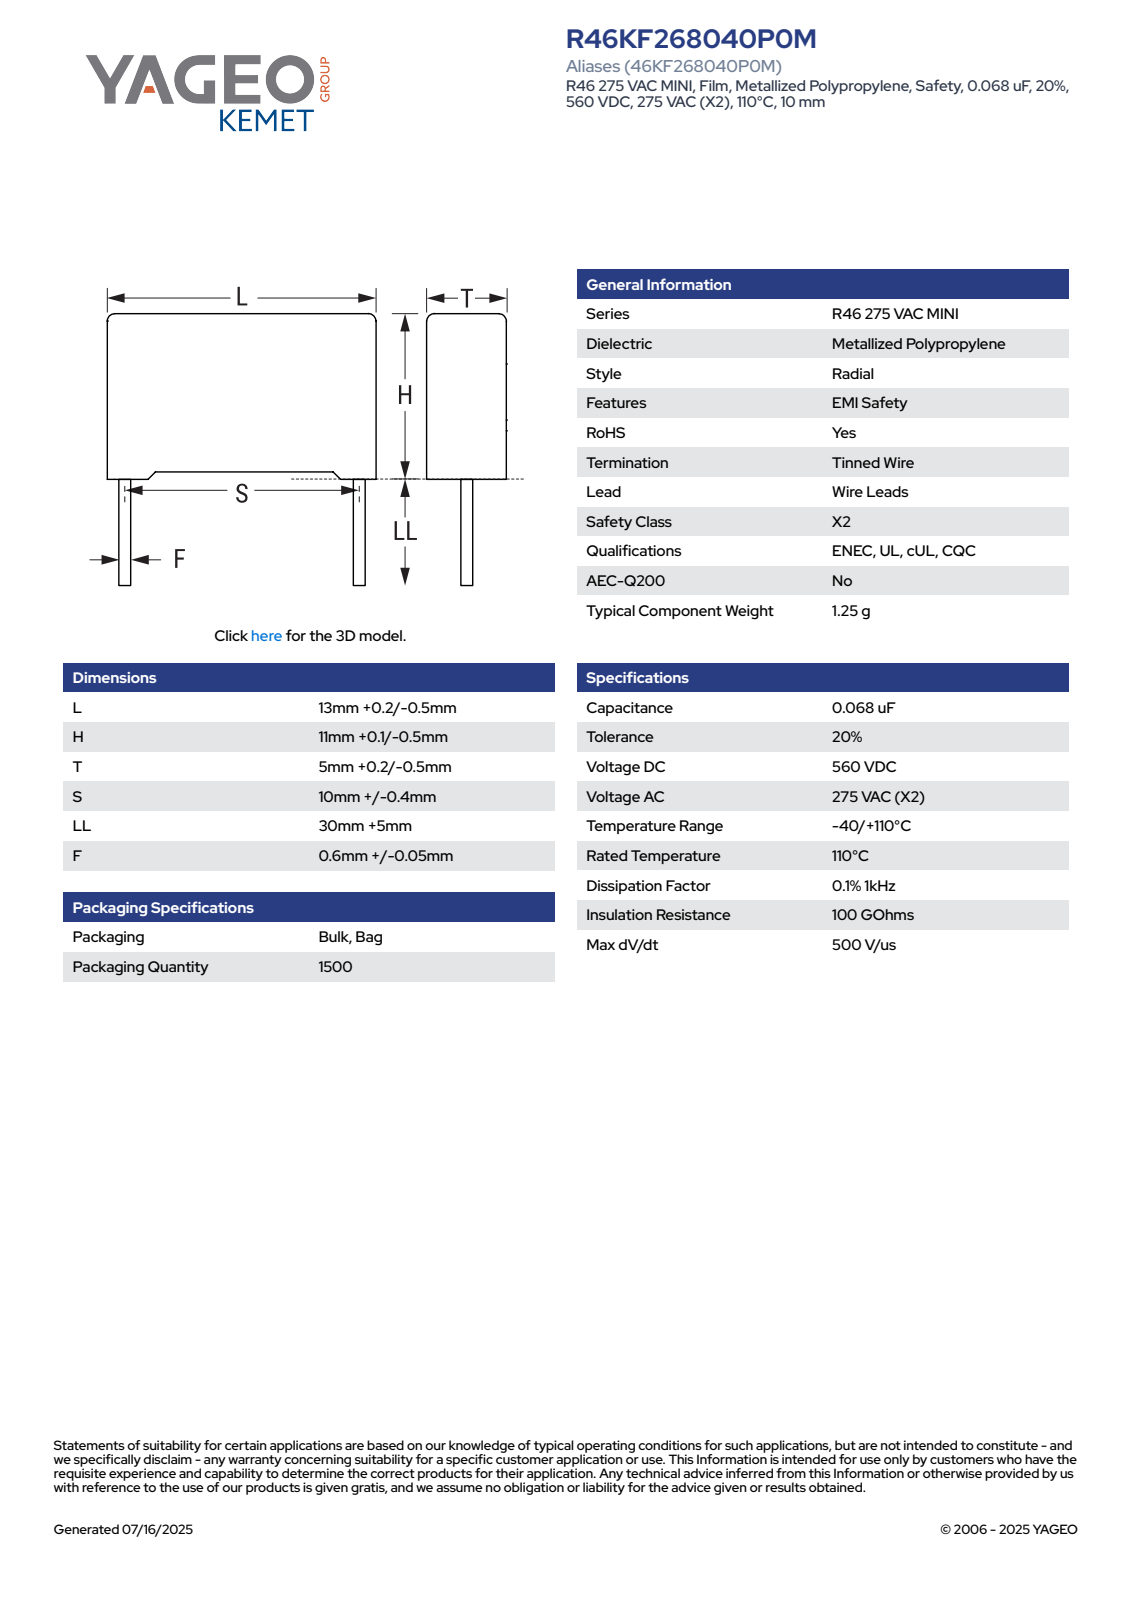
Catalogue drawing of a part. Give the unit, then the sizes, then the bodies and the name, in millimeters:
Units: millimetres
Overall size (bounding box): 46.1 × 13.2 × 5.21
Round bosses / shafts (diameter × count): ⌀0.65 ×2
Partial cylindrical surfaces — rounded edges, fillets, slot ends (radius × count): R0.5 ×4
Main face-to-face distances: 5.2, 13.2, 10.35, 0.44, 4.76, 0.75, 11.1, 4.32, 12.76, 0.37
Volume: 742 mm³ · Surface area: 712 mm²
Bodies: 4 solids, 85 faces (77 planar, 8 cylindrical, 0 other)
Part name (STEP PRODUCT): CFR_RB2_13X11X5_L13.2H11.1T5.2S10LL35F0.65
STEP written by: SolidWorks 2021 (AUTOMOTIVE_DESIGN)
